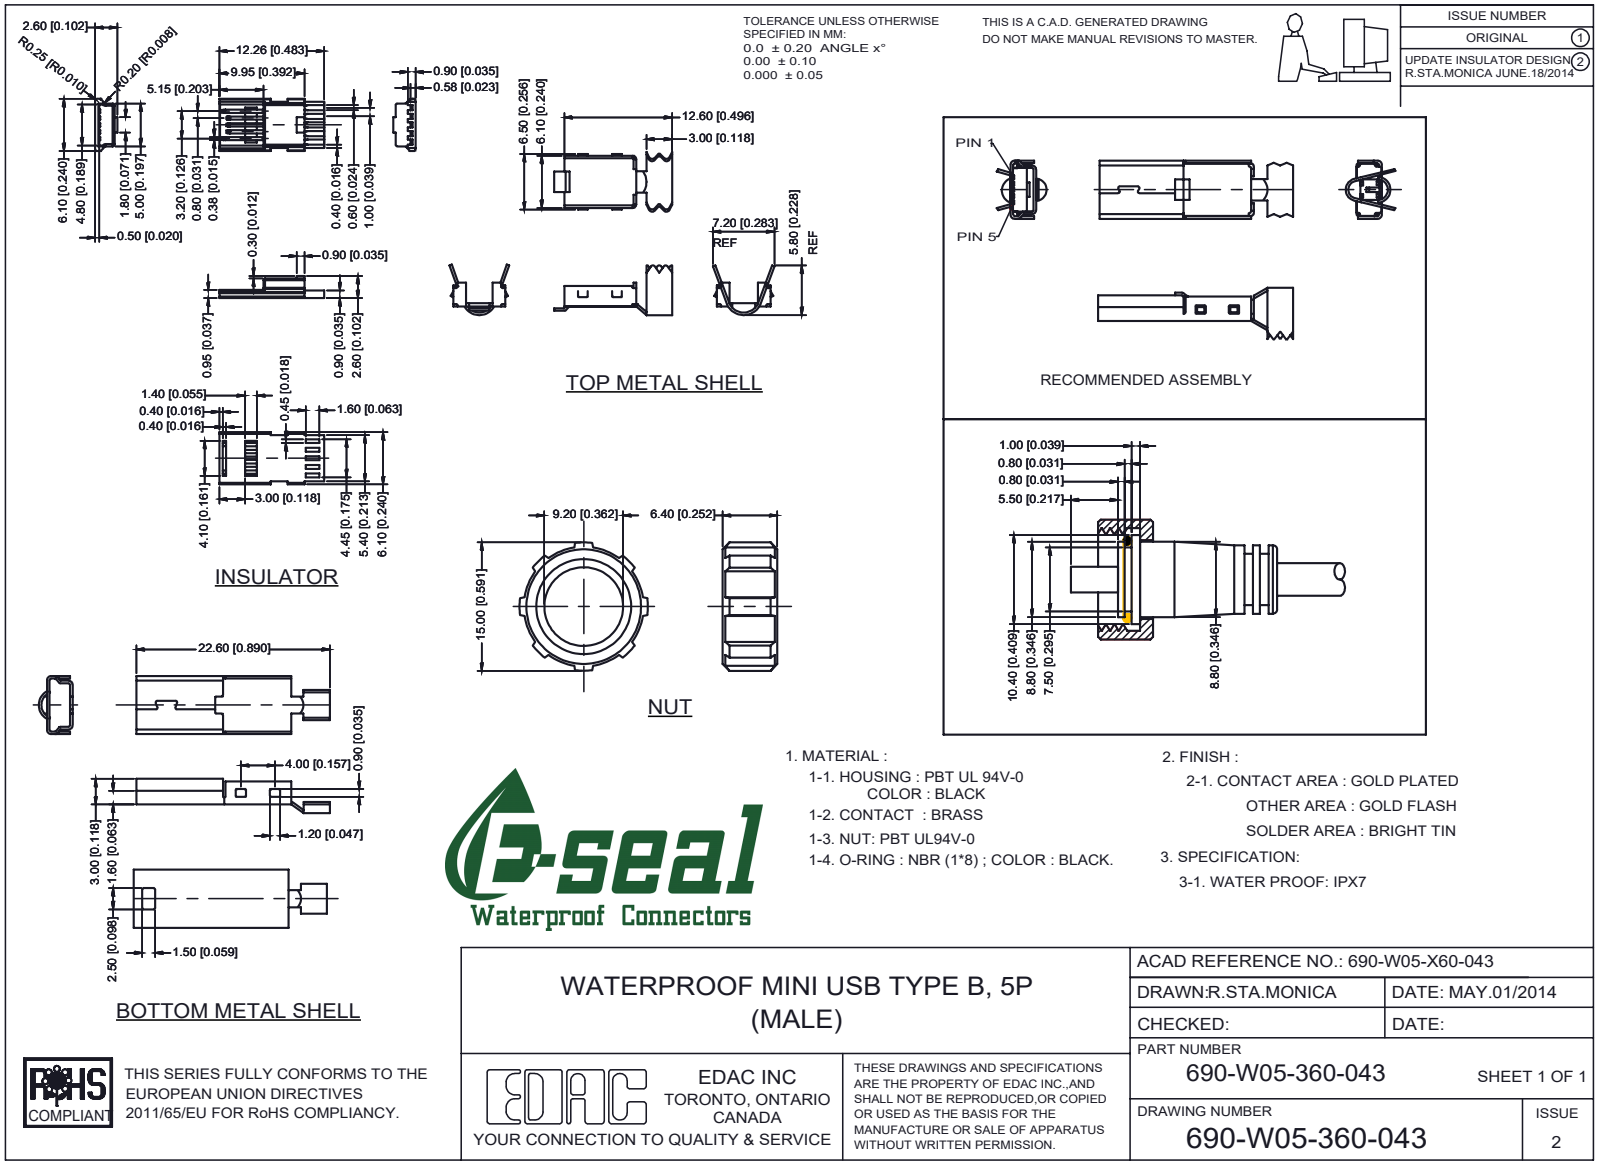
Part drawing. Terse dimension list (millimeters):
name: USB CONTACTS 690-W05-X60-043; OVERMOULD 690-W05-X60-043; 690-W05-260-043; USB SHELL1 690-W05-X60-043 (+4 more)
written by: SolidWorks 2020 (AUTOMOTIVE_DESIGN)
unit: mm
bodies: 9 solids, 568 faces (343 planar, 190 cylindrical, 35 other)
size: 32.03 × 15 × 15
volume: 1 732 mm³; area: 2 732 mm²
holes: 15× ⌀0.5, 1× ⌀1.54, 1× ⌀9.2, 1× ⌀10.85
bosses: 1× ⌀10.4, 1× ⌀8.8, 1× ⌀8, 1× ⌀7.5, 1× ⌀6, 1× ⌀3.82
rounds: 26× R0.15, 13× R0.2, 9× R0.5, 7× R0.25, 7× R0.3, 4× R0.55, 2× R0.1, 2× R0.22
face distances: 1, 2.7, 0.31, 2.39, 2.6, 0.35, 4.1, 2.3, 0.8, 1.8
hole spacings: 0.8, 1.6, 2.76, 3.09, 3.58, 6.18, 2.64, 2.4
